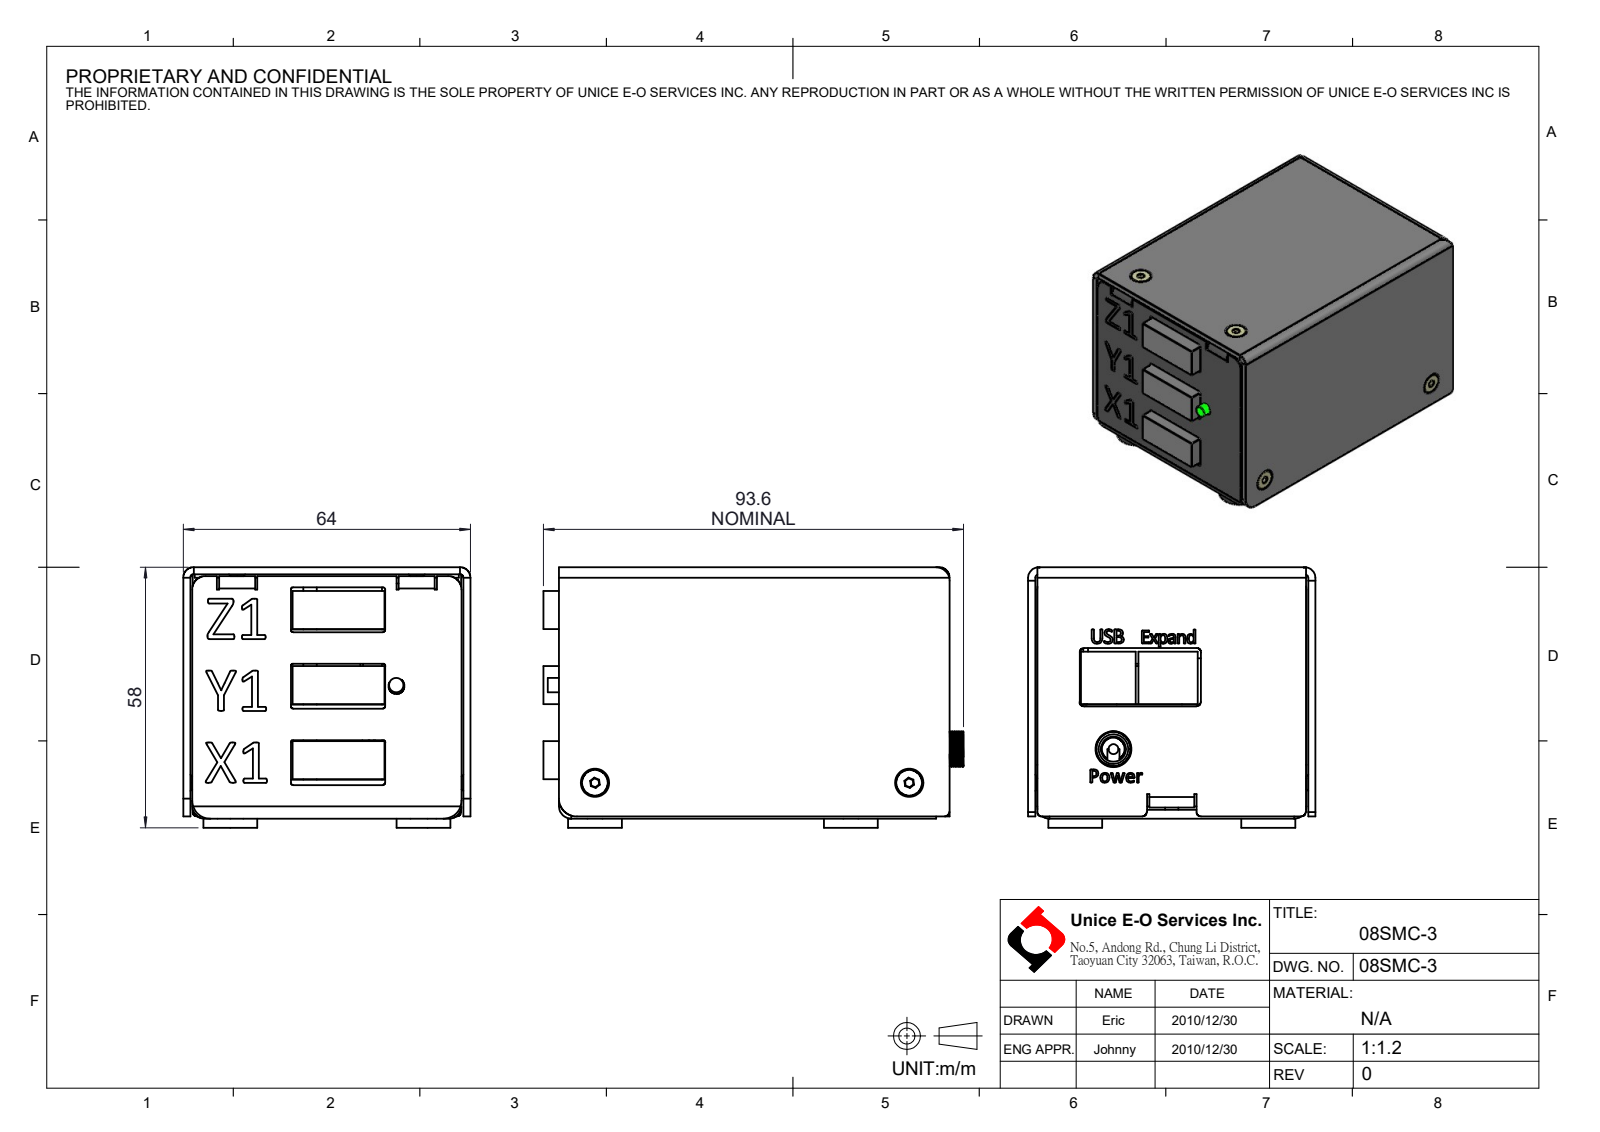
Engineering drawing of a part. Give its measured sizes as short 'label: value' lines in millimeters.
name: 08SMC-3
written by: SolidWorks 2016 (CONFIG_CONTROL_DESIGN)
unit: mm
bodies: 39 solids, 2217 faces (579 planar, 766 cylindrical, 872 other)
size: 93.6 × 64 × 58
volume: 85 555 mm³; area: 97 132 mm²
holes: 9× ⌀2.5, 9× ⌀3.6, 5× ⌀3.5, 1× ⌀5.6, 1× ⌀8
bosses: 9× ⌀5.78, 9× ⌀2.93, 4× ⌀12, 4× ⌀3, 4× ⌀2.75, 4× ⌀2.45, 3× ⌀8, 1× ⌀11
rounds: 16× R0.5, 9× R1, 8× R0.74, 6× R1.2, 4× R2.34, 4× R2.74, 4× R3, 3× R4
face distances: 1.6, 16.7, 1.7, 2, 62.4, 33.4, 15, 18.4, 56, 5
hole spacings: 1.5, 25.12, 41.5, 43, 57, 57.02, 70.51, 71.4
